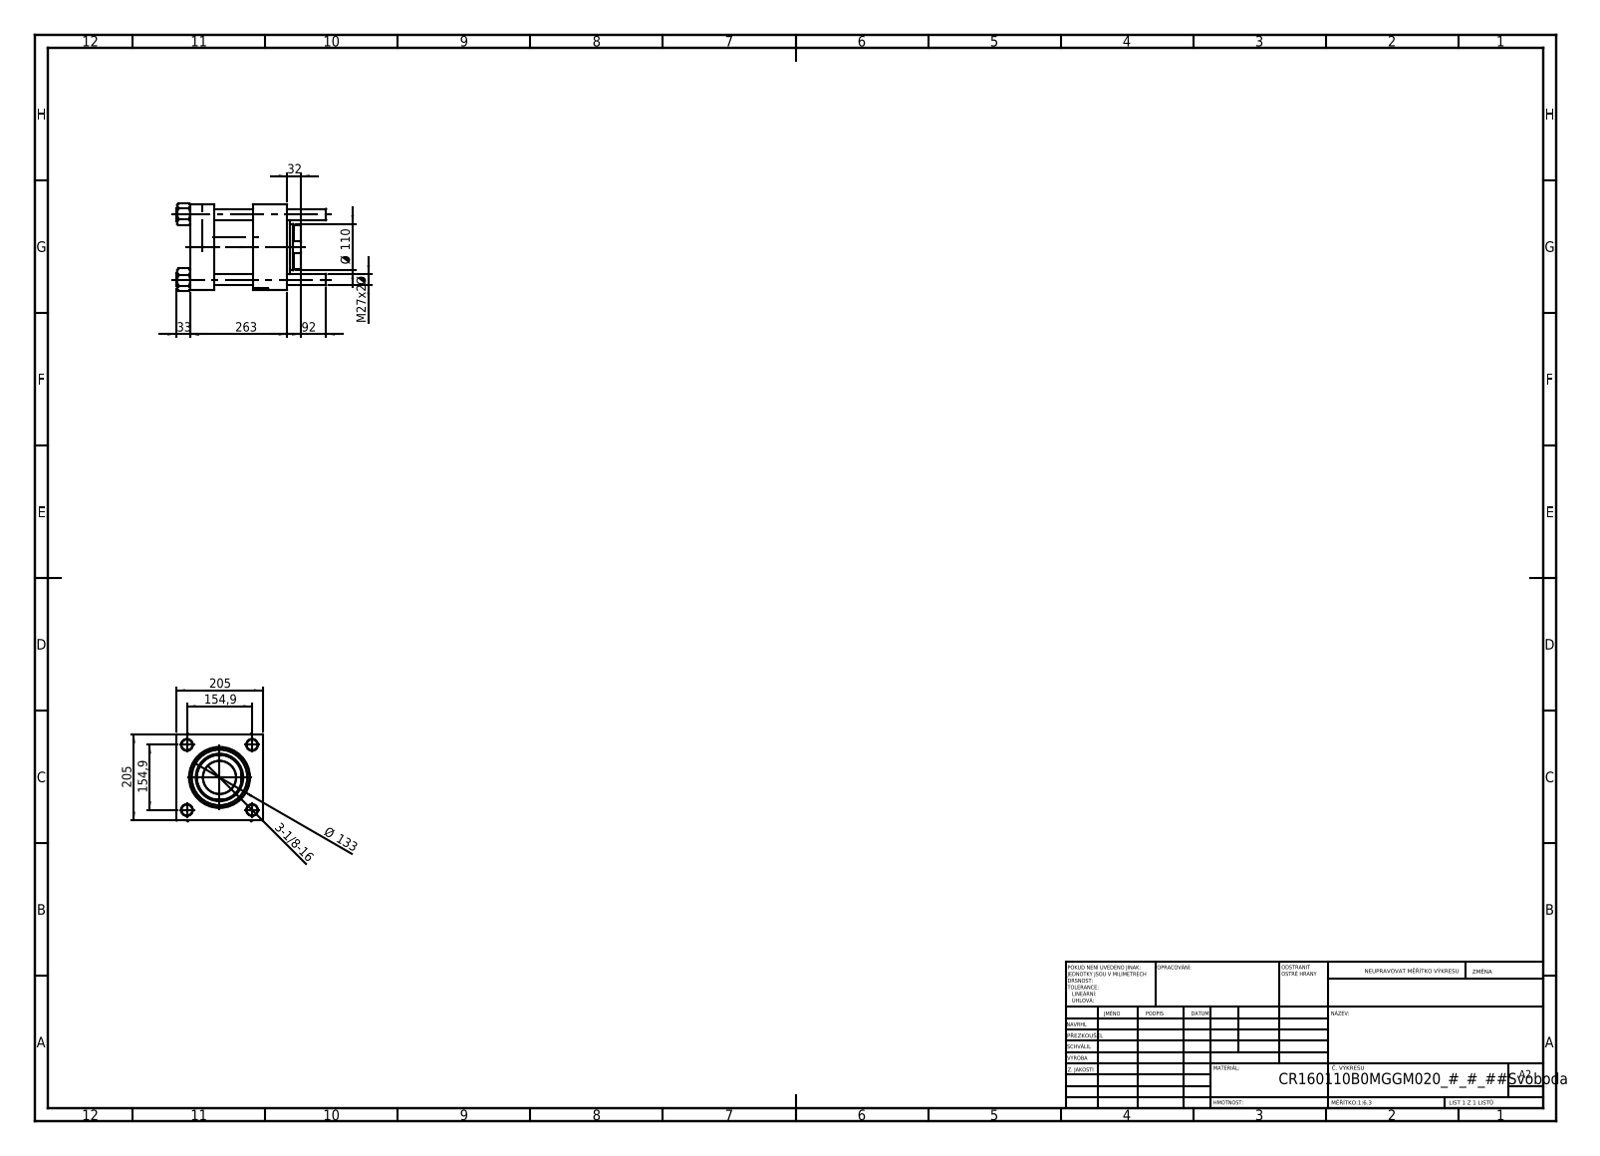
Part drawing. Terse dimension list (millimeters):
name: NUT_M5_B; V215CR_B_TYCINKA; V215CR_VCP_B; V215_VC_A (+1 more)
written by: SolidWorks 2019 (CONFIG_CONTROL_DESIGN)
unit: mm
bodies: 11 solids, 1206 faces (479 planar, 79 cylindrical, 648 other)
size: 356 × 207.94 × 205
volume: 7 952 000 mm³; area: 782 238 mm²
holes: 5× ⌀27, 2× ⌀7, 2× ⌀33.24, 1× ⌀45, 1× ⌀78.5, 1× ⌀110, 1× ⌀113, 1× ⌀120, 1× ⌀142, 1× ⌀160
bosses: 4× ⌀30, 1× ⌀166, 1× ⌀133
rounds: 1× R54
face distances: 205, 58, 92, 173, 150, 231, 81, 202.3, 144.3, 52.3
hole spacings: 109.53, 154.9, 219.06, 154.24
